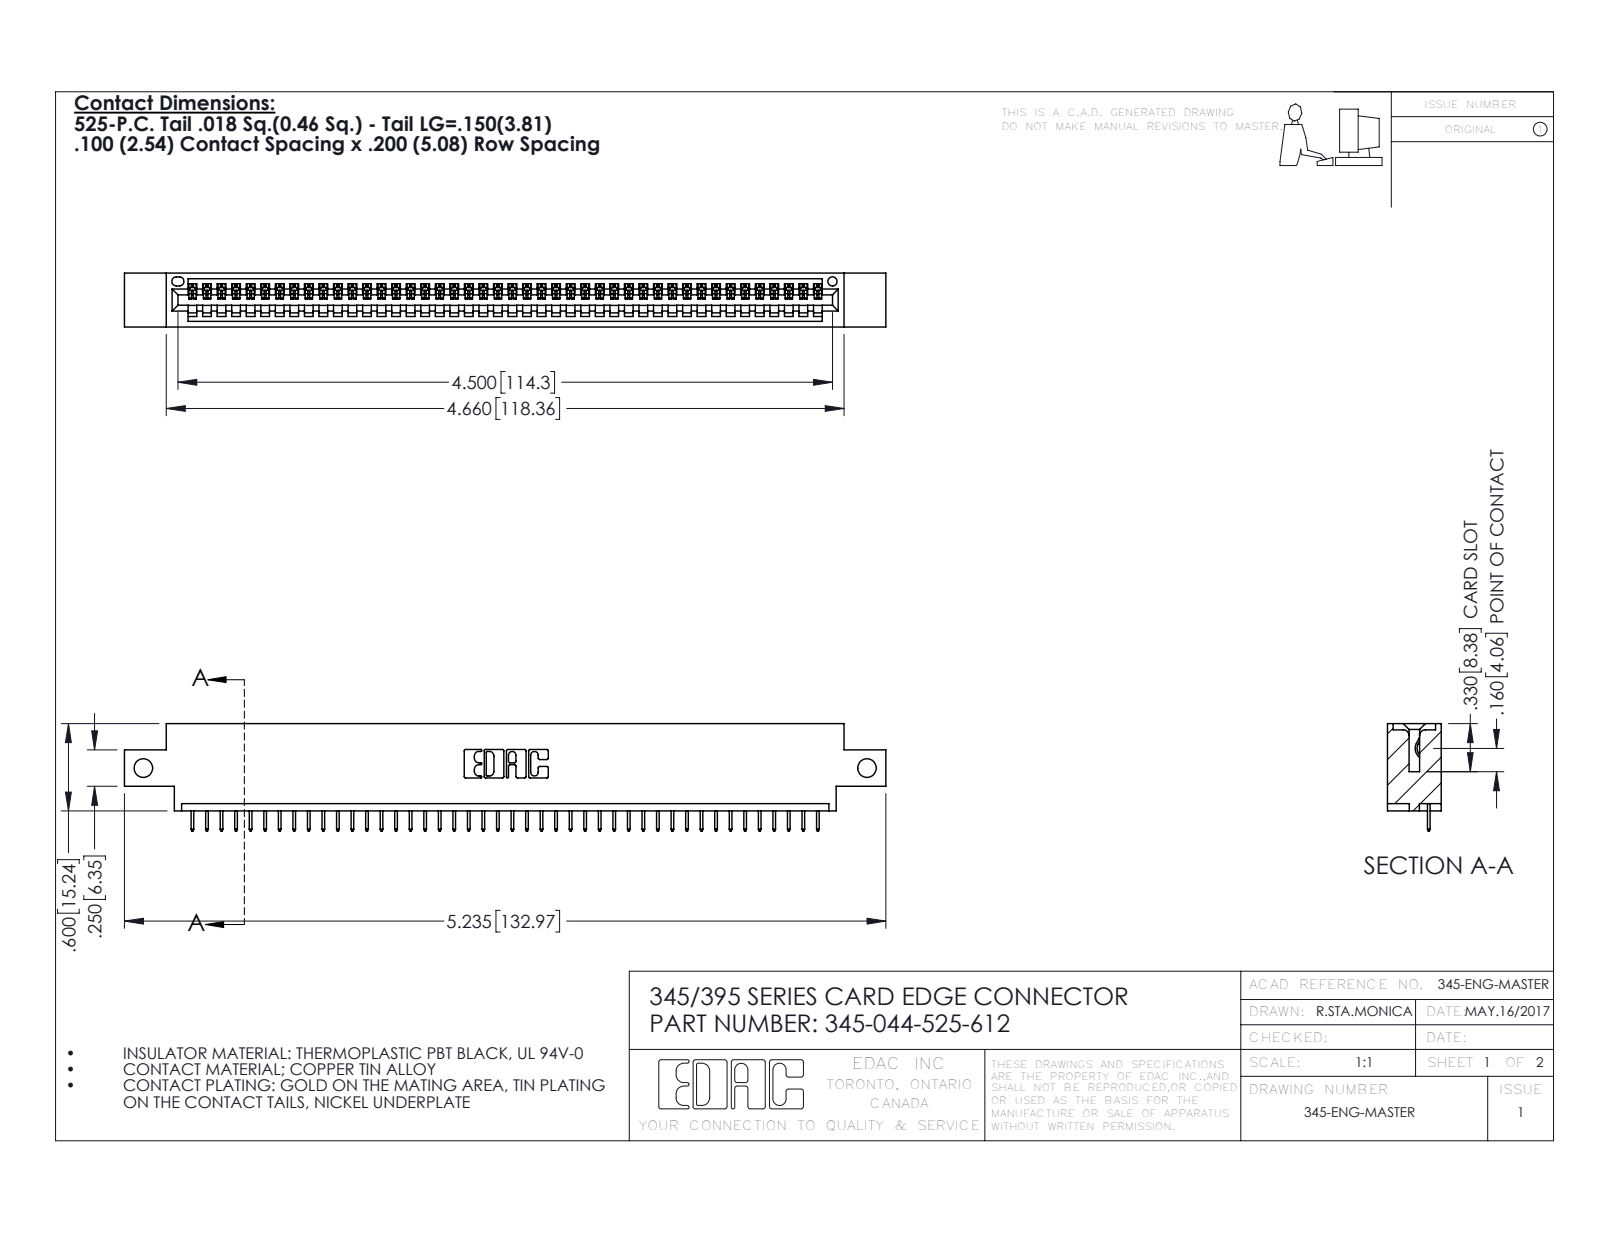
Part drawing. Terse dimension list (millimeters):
name: 345-044-525-612; 345-292-001_345-293-125; 345 Part_0.170 Offset - Side Mount
written by: SolidWorks 2020 (CONFIG_CONTROL_DESIGN)
unit: mm
bodies: 45 solids, 2858 faces (2108 planar, 750 cylindrical, 0 other)
size: 133 × 18.7 × 9.4
volume: 12 300 mm³; area: 15 710 mm²
holes: 2× ⌀3.3, 1× ⌀1.6
rounds: 88× R0.2, 22× R0.3, 6× R0.2, 6× R0.8, 3× R0.7, 2× R0.8, 2× R1, 1× R0.4
face distances: 1.8, 7.6, 9.4, 5.1, 2.5, 6.9, 0.6, 5.7, 4.4, 1.8
hole spacings: 126.4
